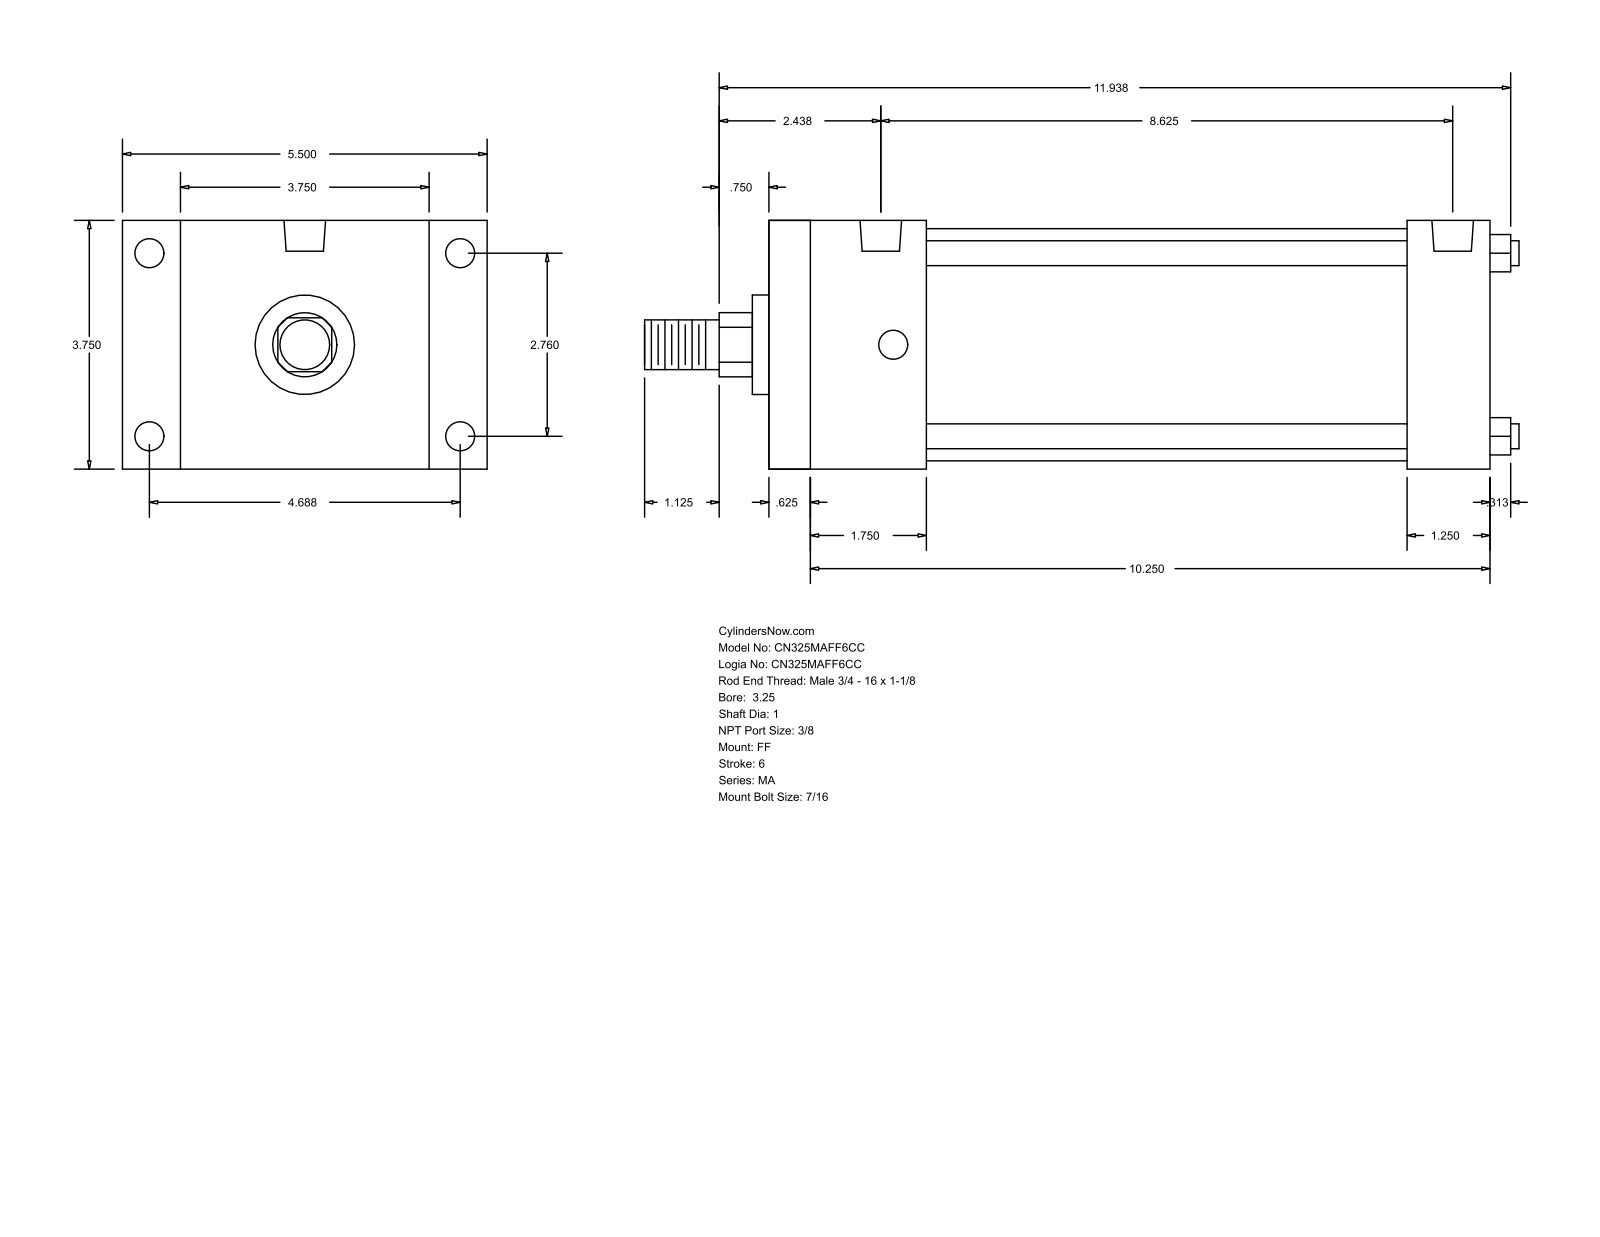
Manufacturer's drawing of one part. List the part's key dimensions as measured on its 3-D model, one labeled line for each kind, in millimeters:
Part name (STEP PRODUCT): MA_FF__0325_1
STEP written by: GSSL Pune (CONFIG_CONTROL_DESIGN)
Units: millimetres
Bodies: 0 solids, 92 faces (64 planar, 28 cylindrical, 0 other)
Overall size (bounding box): 334.96 × 139.7 × 95.25
Round holes (diameter × count): ⌀11.11 ×8, ⌀15.93 ×2
Round bosses / shafts (diameter × count): ⌀9.53 ×4, ⌀88.9 ×1, ⌀38.1 ×1, ⌀25.4 ×1, ⌀19.05 ×1
Partial cylindrical surfaces — rounded edges, fillets, slot ends (radius × count): R12.29 ×1
Main face-to-face distances: 95.24, 276.22, 15.87, 260.35, 22.23, 117.47, 60.33, 244.47, 44.46, 228.6
Hole centre spacings: 4.76, 70.1, 119.06, 138.16, 209.56, 214.32, 219.08
